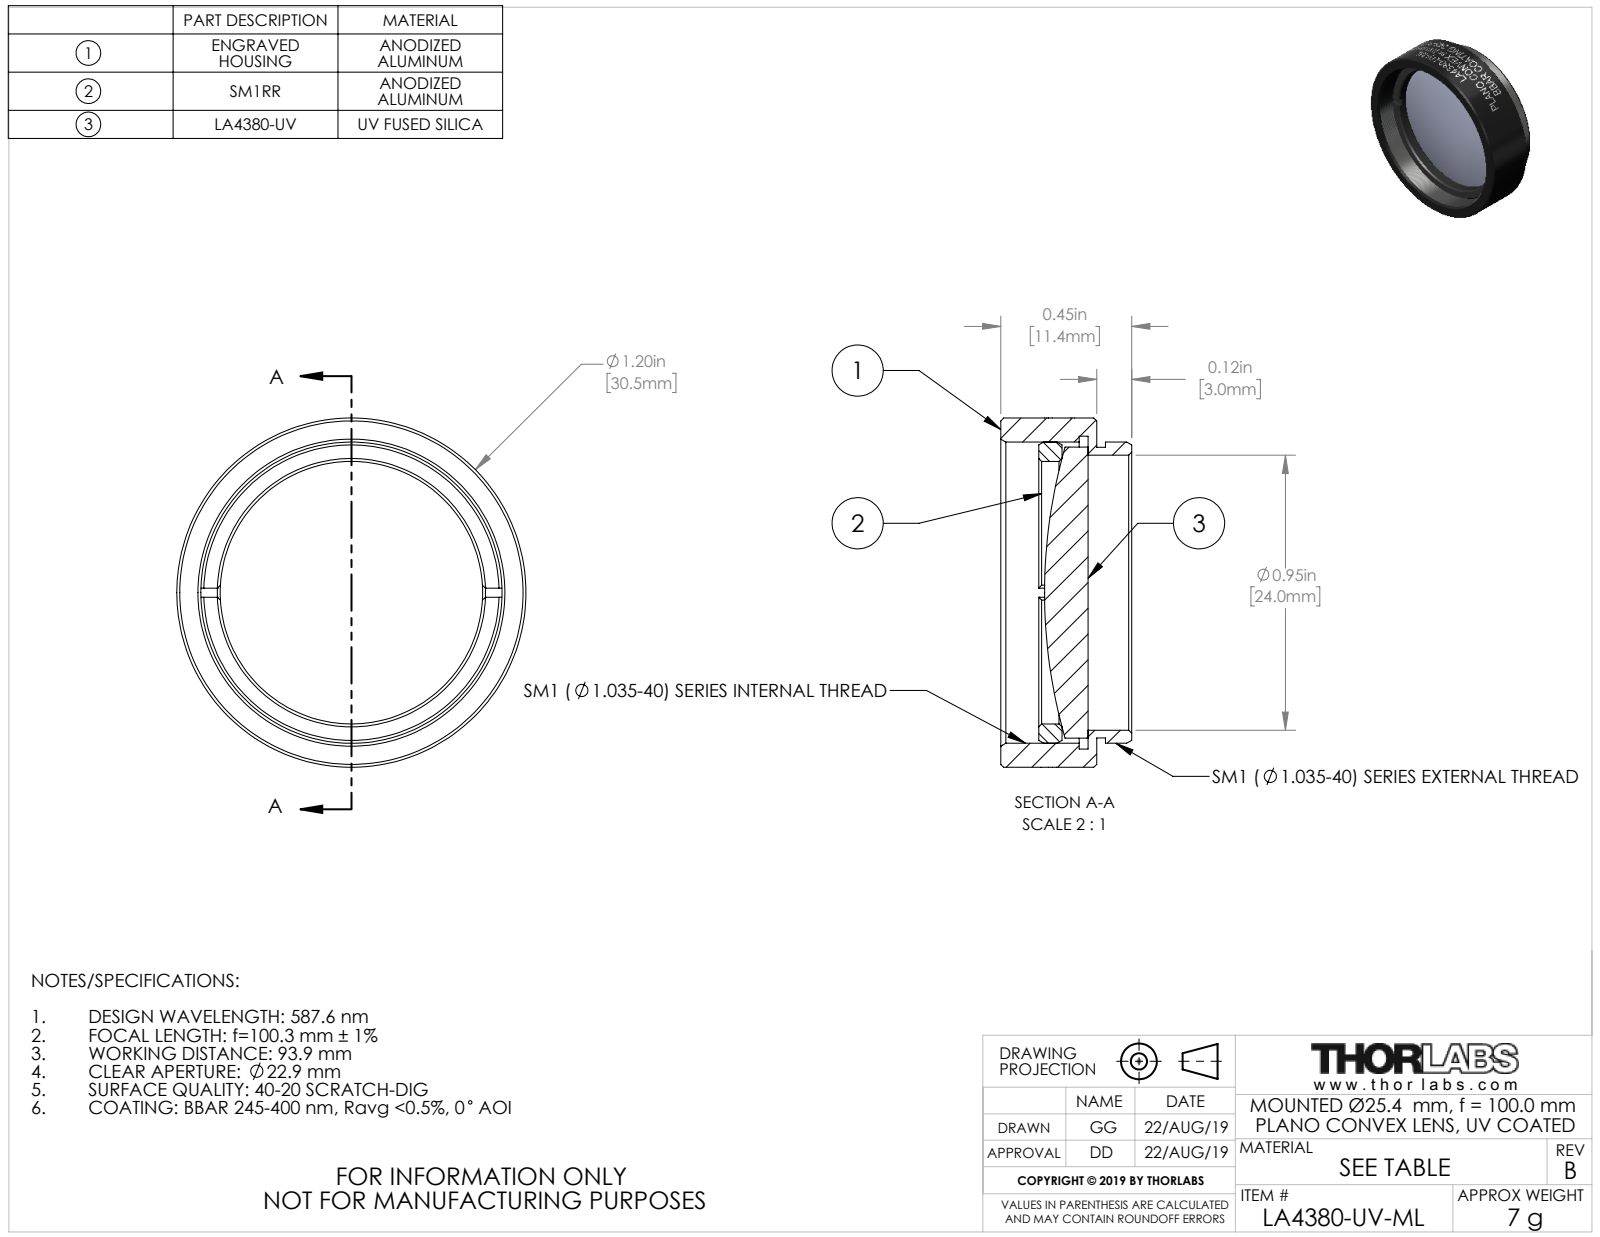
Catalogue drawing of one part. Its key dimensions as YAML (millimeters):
part_name: "24457-E0W"
step_written_by: "SolidWorks 2018 (CONFIG_CONTROL_DESIGN)"
units: millimeters
bodies: {solids: 3, faces: 156, planar: 20, cylindrical: 112, other: 24}
overall_size: [30.48, 30.48, 11.43]
volume: 3551
surface_area: 4323
round_holes:
  - {diameter: 22.91, count: 1}
  - {diameter: 24, count: 1}
  - {diameter: 26.29, count: 1}
  - {diameter: 27.3, count: 1}
round_bosses_or_shafts:
  - {diameter: 30.48, count: 1}
  - {diameter: 26.29, count: 1}
  - {diameter: 25.4, count: 1}
  - {diameter: 25.37, count: 1}
face_to_face_distances: [0.76, 8.38, 7.62, 3.03, 2.27, 5.35, 5.06, 4.3, 2.03, 3.32]
